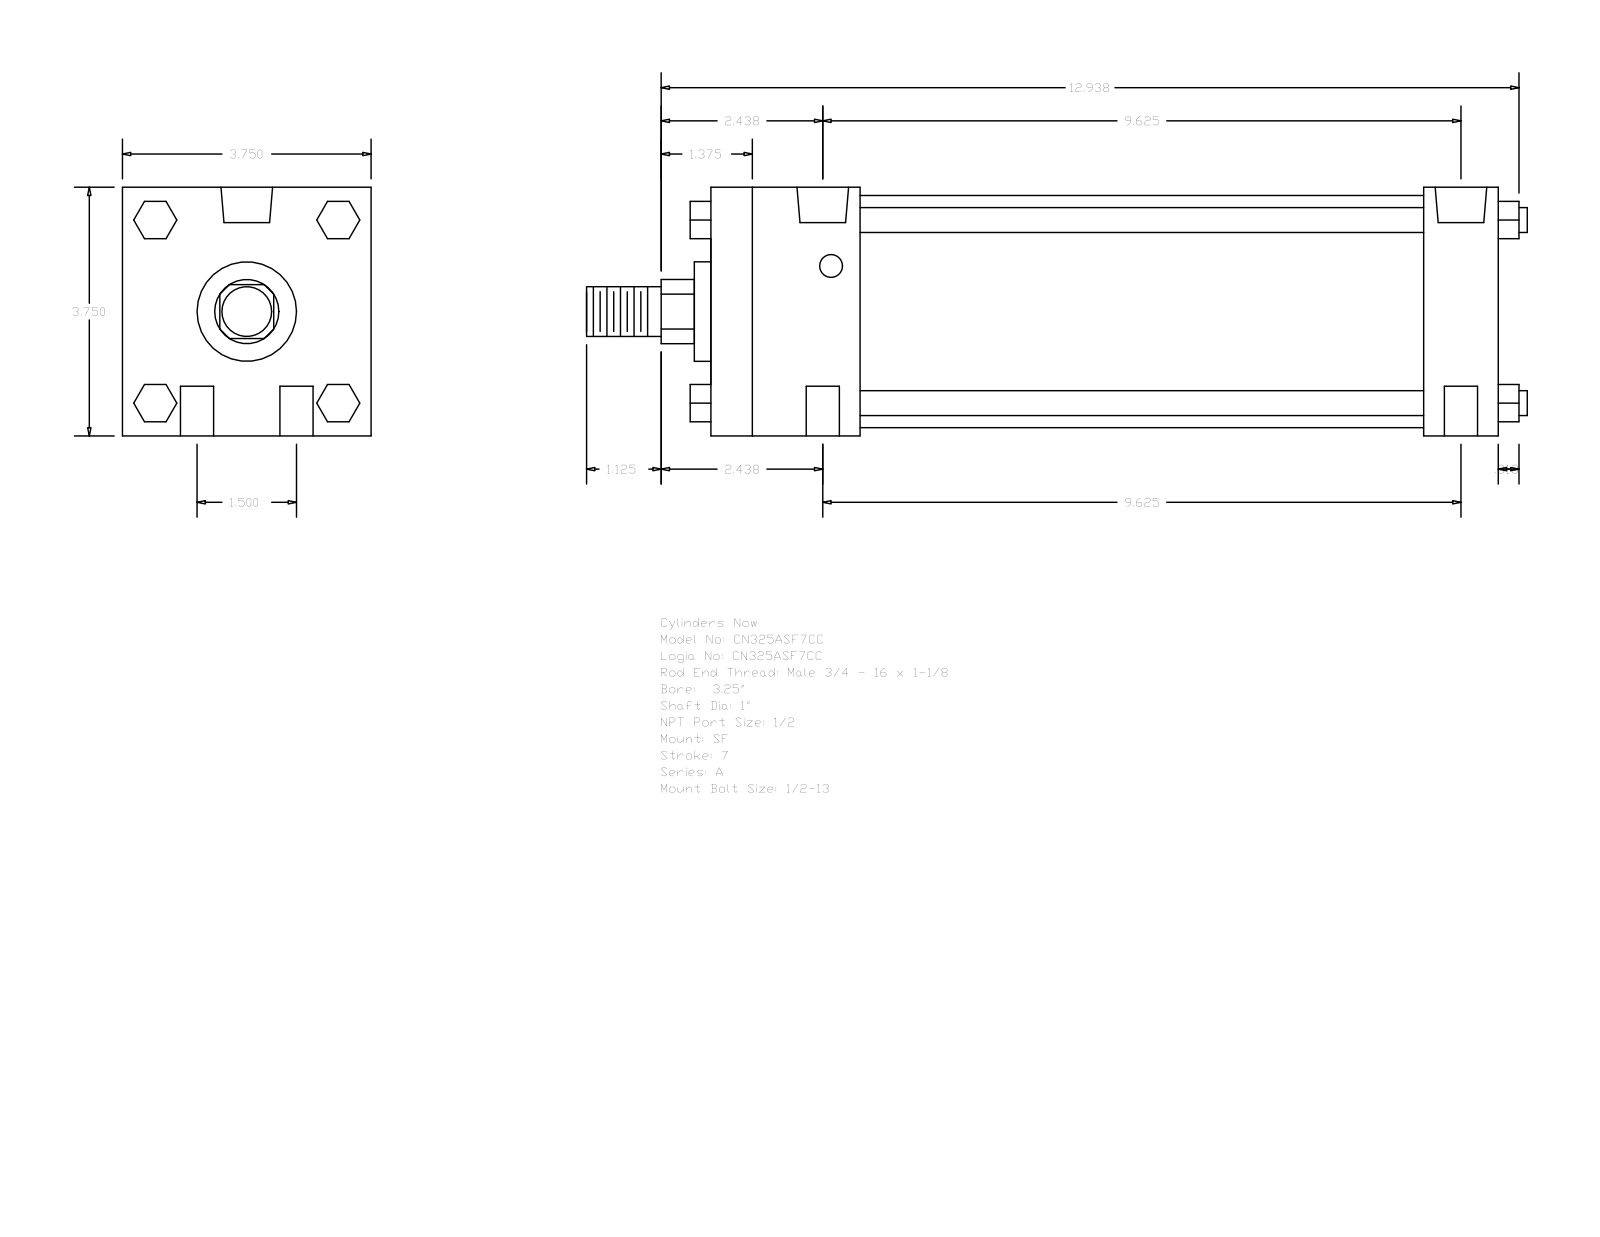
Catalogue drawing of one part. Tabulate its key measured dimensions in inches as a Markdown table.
| quantity | value |
| --- | --- |
| part name | A_SF__0325_1 |
| STEP written by | GSSL Pune (CONFIG_CONTROL_DESIGN) |
| units | inches |
| bodies | 0 solids, 124 faces (94 planar, 30 cylindrical, 0 other) |
| overall size | 14.187 × 3.75 × 3.75 |
| round holes (diameter × count) | 0.5 × 4, 0.344 × 2, 0.778 × 2 |
| round bosses / shafts (diameter × count) | 0.375 × 4, 3.5 × 1, 1.5 × 1, 1 × 1, 0.75 × 1 |
| partial cylindrical surfaces (radius × count) | 0.484 × 1 |
| main face-to-face distances | 3.75, 11.875, 10.75, 1.125, 2.25, 8.5, 9.625, 0.562, 1.38, 2.39 |
| hole center spacings | 0.75, 9.654, 9.625, 1.5, 9.741, 9.375 |
